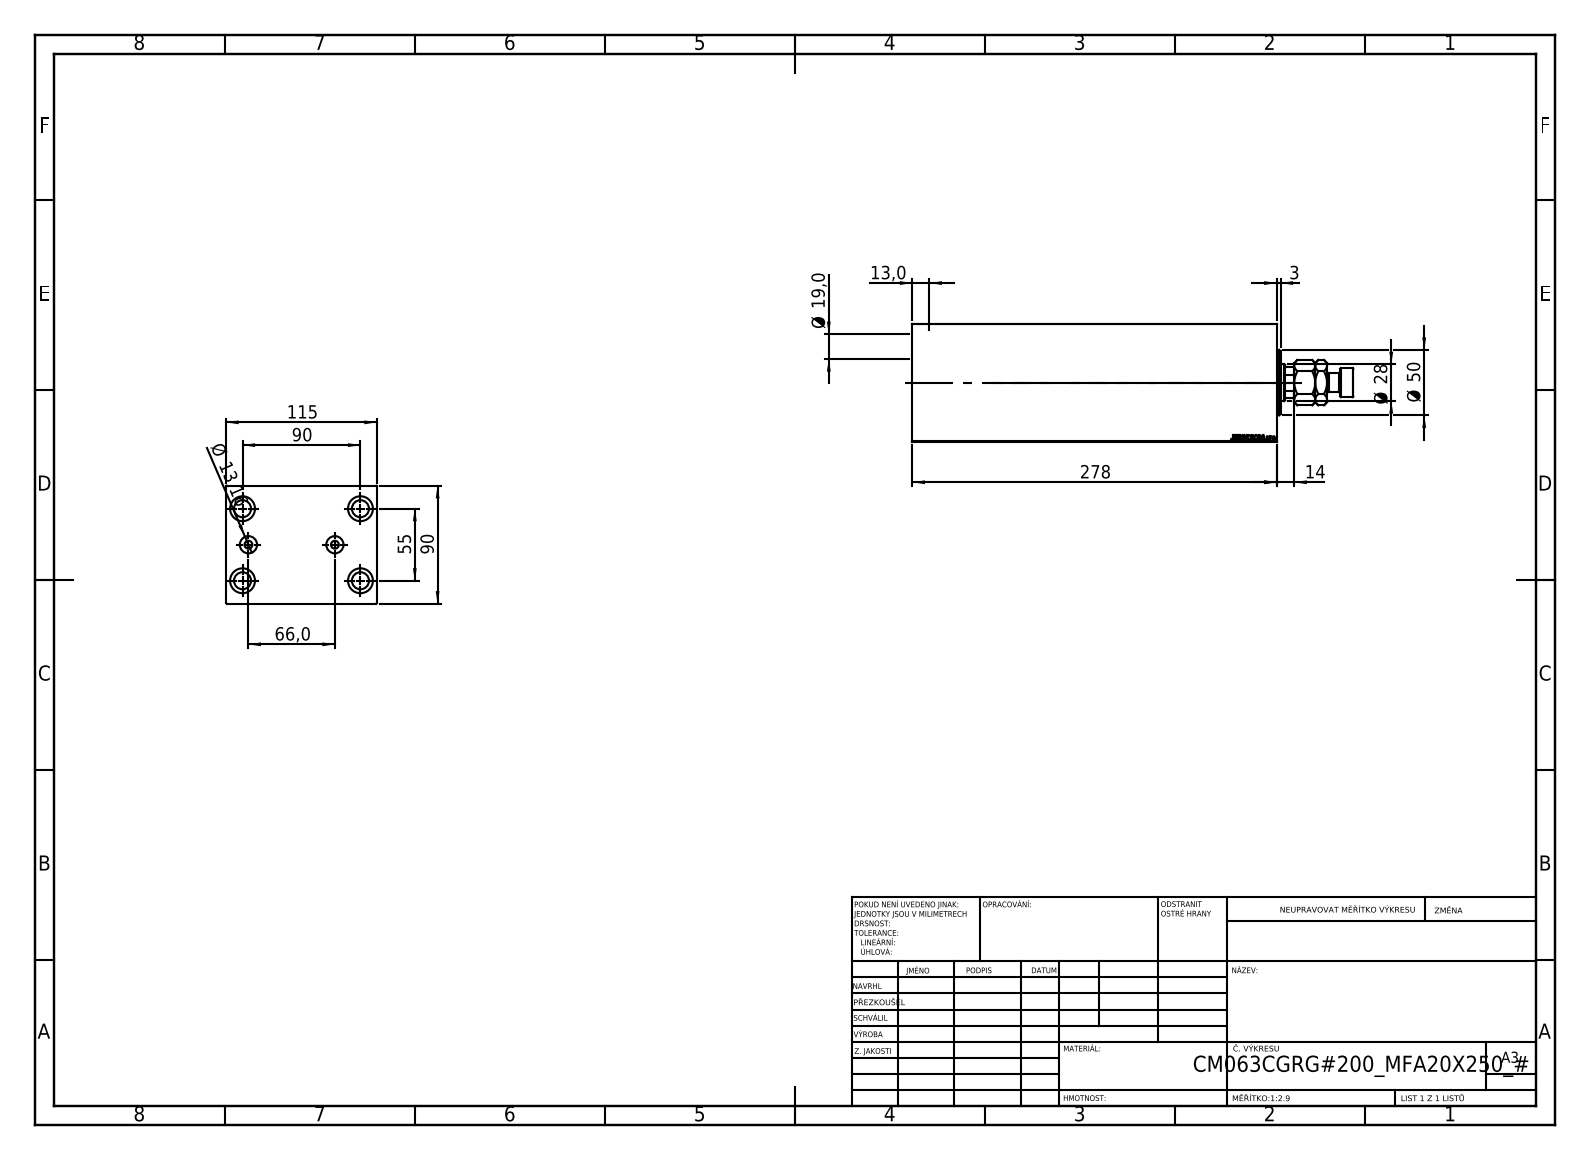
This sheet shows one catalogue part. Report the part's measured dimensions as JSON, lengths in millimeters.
{"part_name": "MFA; V450CM_C_VCP; V450CM_VC_B; V450CM_C_Body", "step_written_by": "SolidWorks 2019 (CONFIG_CONTROL_DESIGN)", "units": "millimeters", "bodies": {"solids": 4, "faces": 912, "planar": 424, "cylindrical": 62, "other": 426}, "overall_size": [336.5, 115, 90], "volume_mm3": 2232000, "surface_area_mm2": 292447, "round_holes": [[13, 4], [19, 4], [6, 2], [13.16, 2], [18.5, 1], [28, 1], [31.5, 1], [63, 1], [65, 1], [72, 1]], "round_bosses_or_shafts": [[50, 1], [22, 1], [14, 1]], "partial_cylinders_radius": [[13.5, 1]], "face_to_face_distances": [90, 115, 278, 17.5, 260.5, 13.5, 247, 264.5, 47, 64.5], "hole_center_spacings": [52.74, 27.87, 33.71, 55, 75.67, 89.81, 90, 105.48]}
